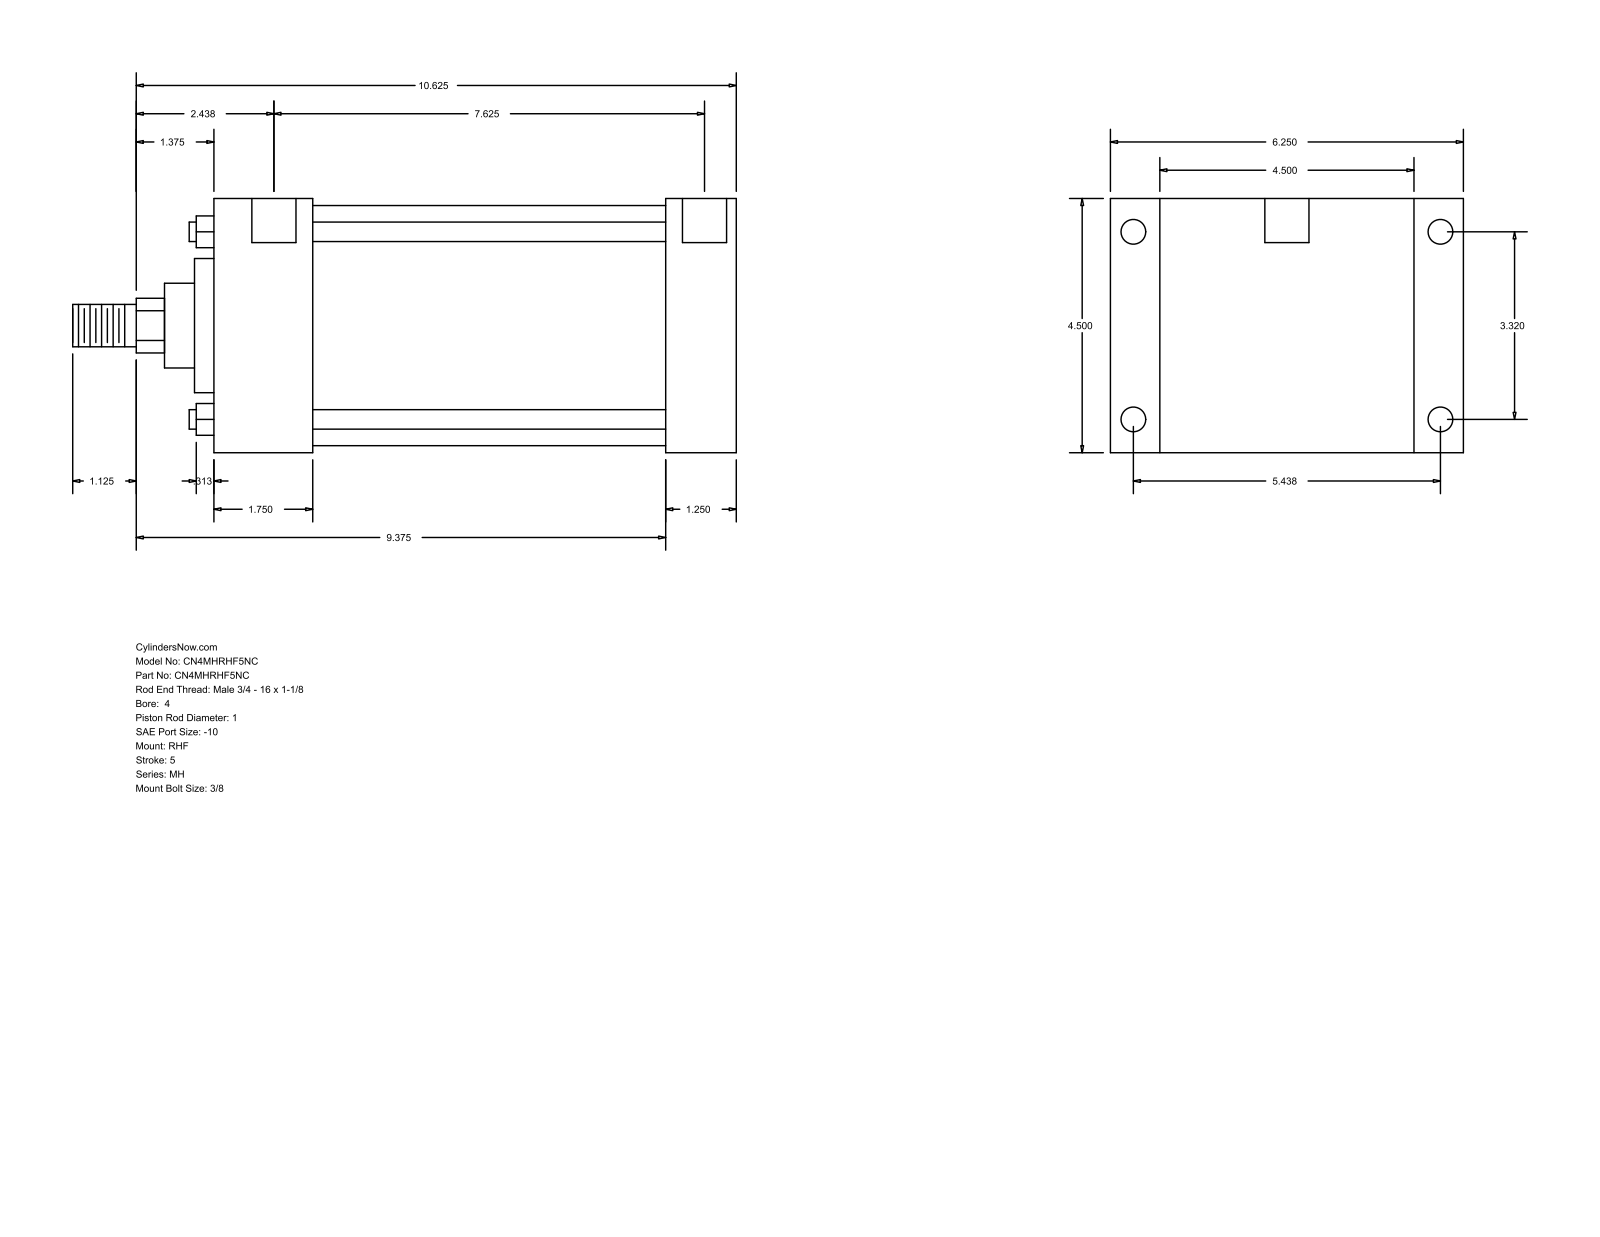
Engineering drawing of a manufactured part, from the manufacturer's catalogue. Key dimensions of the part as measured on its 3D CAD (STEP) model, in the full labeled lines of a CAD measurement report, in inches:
Part name (STEP PRODUCT): MH_RHF__0400_1
STEP written by: GSSL Pune (CONFIG_CONTROL_DESIGN)
Units: inches
Bodies: 0 solids, 90 faces (61 planar, 29 cylindrical, 0 other)
Overall size (bounding box): 11.75 × 6.25 × 4.5
Round holes (diameter × count): ⌀0.344 ×4, ⌀0.438 ×4, ⌀0.781 ×2
Round bosses / shafts (diameter × count): ⌀0.345 ×4, ⌀4.25 ×1, ⌀2.375 ×1, ⌀1.5 ×1, ⌀1 ×1, ⌀0.75 ×1
Partial cylindrical surfaces — rounded edges, fillets, slot ends (radius × count): R0.484 ×1
Main face-to-face distances: 4.5, 9.25, 8, 1.25, 0.875, 5.375, 6.25, 1.75, 7.5, 6.25
Hole centre spacings: 3.32, 5.438, 6.371, 7.75, 0.062, 0.063, 7.625, 7.687
